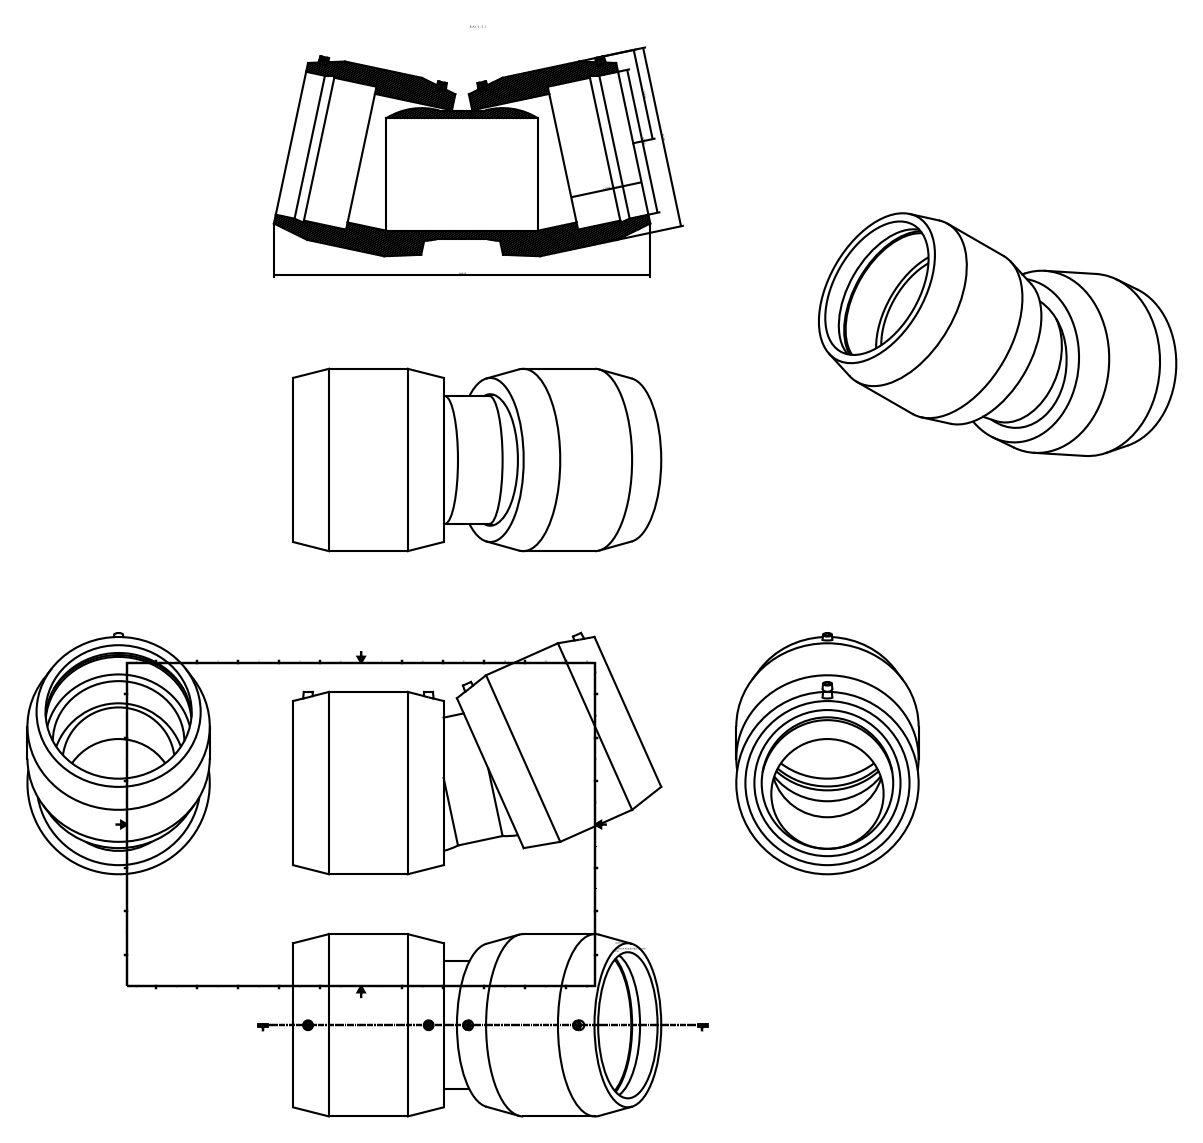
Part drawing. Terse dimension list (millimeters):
name: 4947C4250
written by: Autodesk Inventor 2015 (AUTOMOTIVE_DESIGN)
unit: mm
bodies: 1 solid, 50 faces (20 planar, 18 cylindrical, 12 other)
size: 629.93 × 412.84 × 312
volume: 16 840 000 mm³; area: 1 235 000 mm²
holes: 4× ⌀10, 3× ⌀250, 2× ⌀225, 1× ⌀192.1
bosses: 4× ⌀4, 2× ⌀312, 1× ⌀219.02
face distances: 257.6, 257.74, 123, 134.6, 134.67, 123.07, 49.2, 73.8, 208.4, 208.51
hole spacings: 206.07, 206.08
